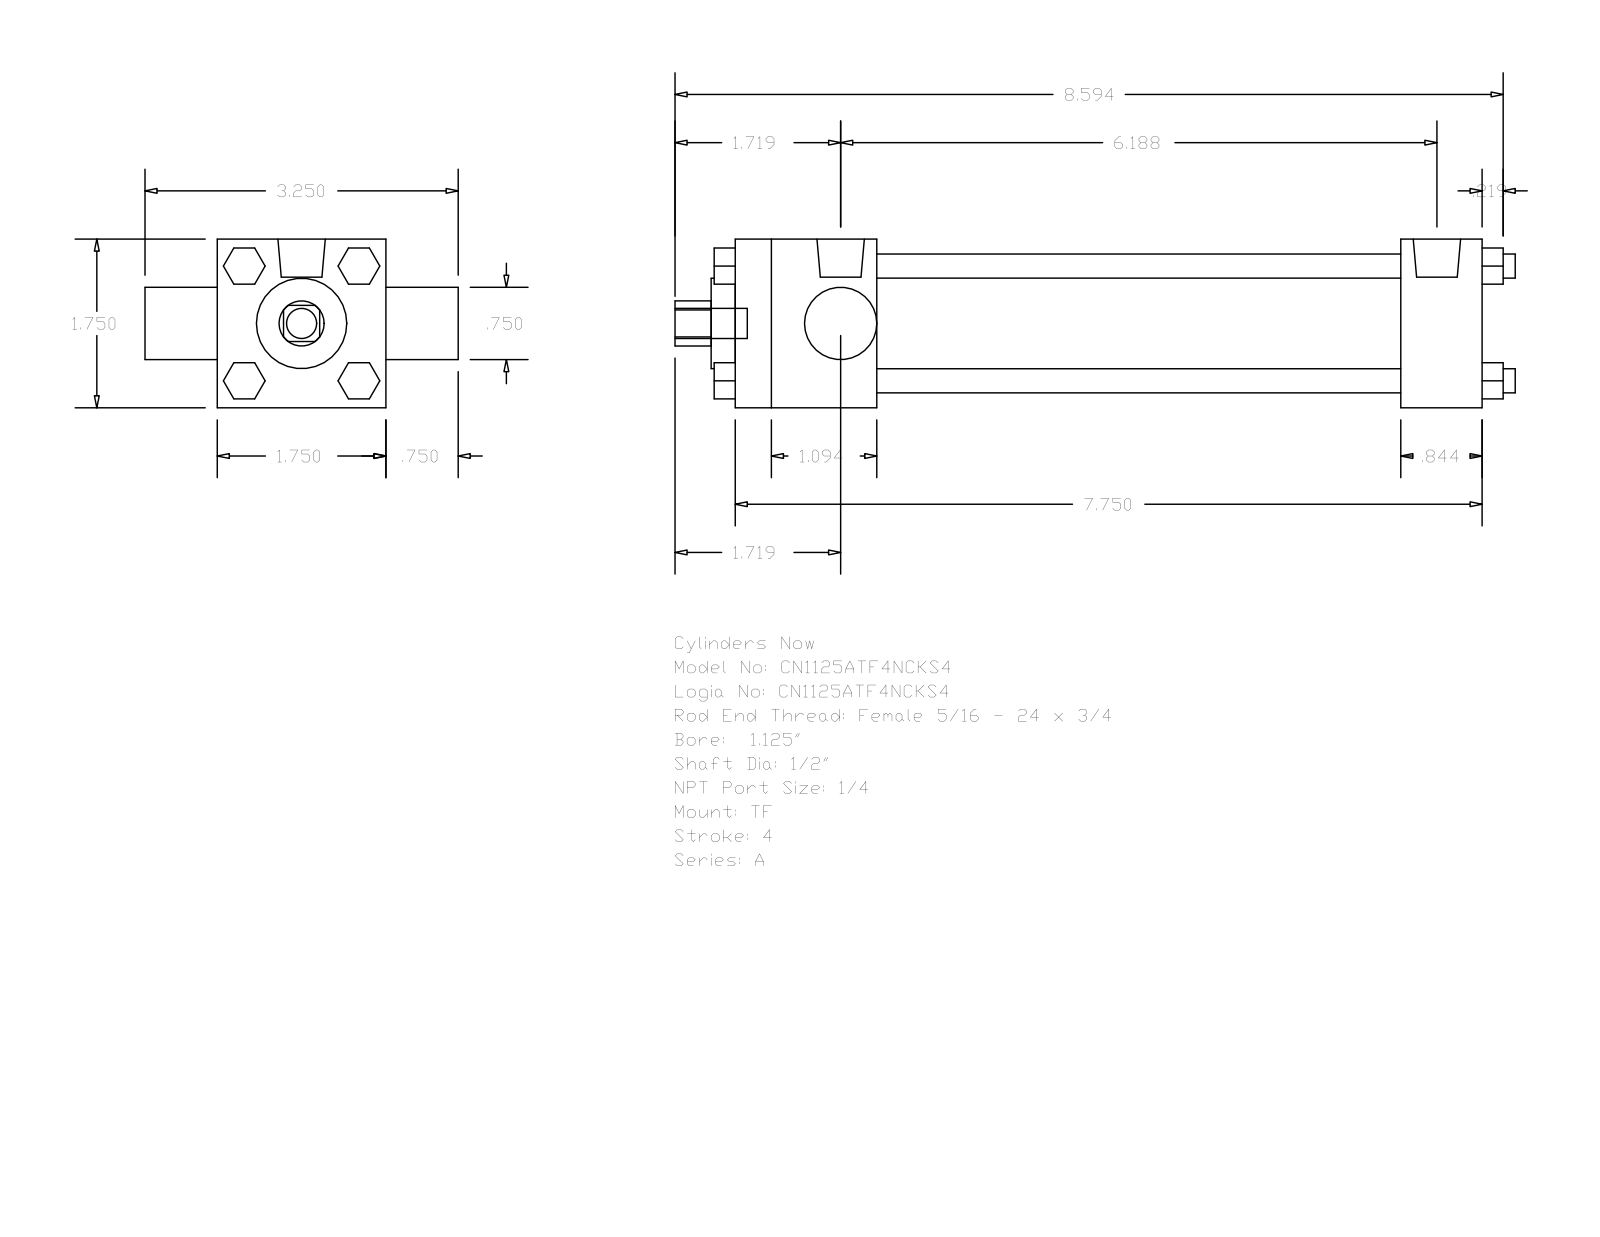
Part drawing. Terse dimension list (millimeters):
name: A_TF__0112_0.5
written by: GSSL Pune (CONFIG_CONTROL_DESIGN)
unit: mm
bodies: 0 solids, 120 faces (92 planar, 28 cylindrical, 0 other)
size: 221.46 × 82.55 × 44.45
holes: 1× ⌀12.7, 1× ⌀19.05, 1× ⌀23.81, 1× ⌀31.88
bosses: 4× ⌀6.35, 3× ⌀5.56, 2× ⌀12.49, 1× ⌀7.94
rounds: 1× R5.94
face distances: 44.46, 196.84, 175.41, 21.43, 37.3, 138.11, 159.54, 19.04, 63.5, 9.53
